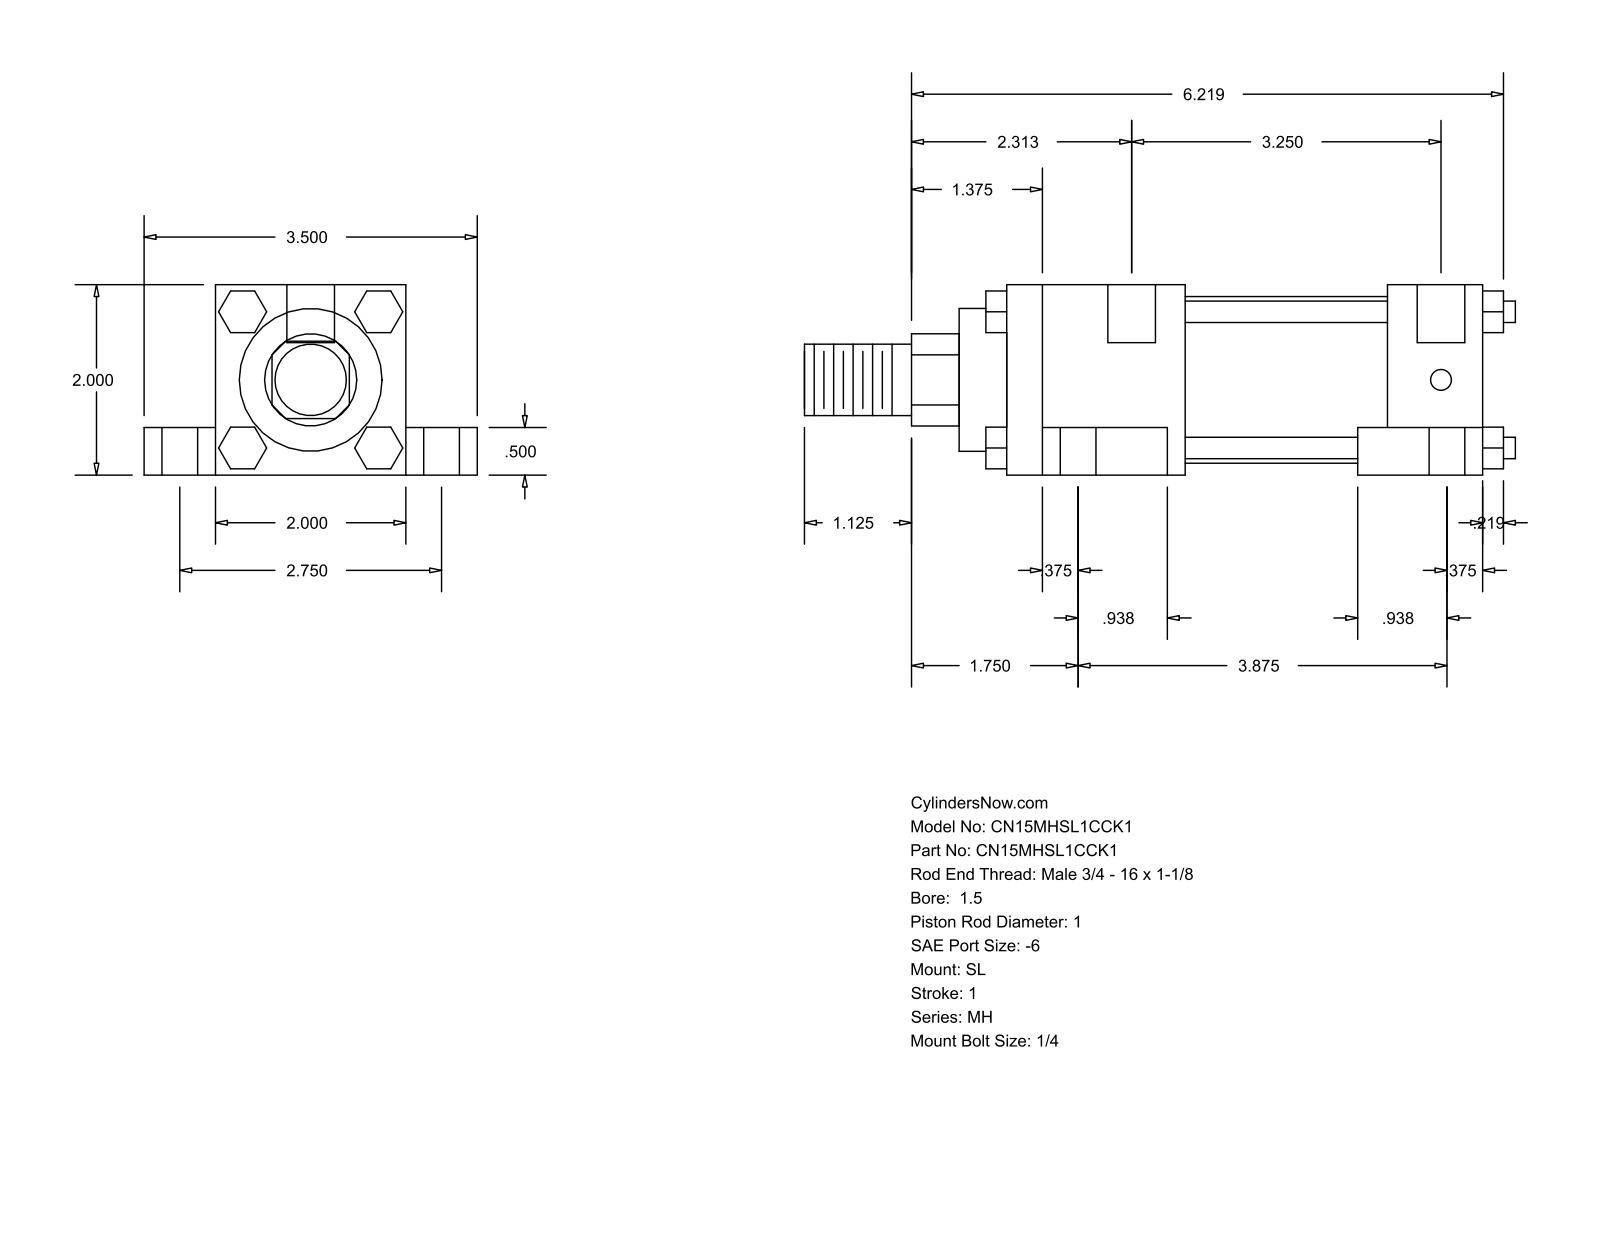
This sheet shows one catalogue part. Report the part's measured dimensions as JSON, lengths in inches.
{"part_name": "MH_SL__0150_1", "step_written_by": "GSSL Pune (CONFIG_CONTROL_DESIGN)", "units": "inches", "bodies": {"solids": 0, "faces": 148, "planar": 112, "cylindrical": 36, "other": 0}, "overall_size": [7.469, 3.5, 2], "round_holes": [[0.219, 4], [0.375, 4], [0.625, 4], [0.5, 2]], "round_bosses_or_shafts": [[0.225, 4], [1.75, 1], [1.5, 1], [1, 1], [0.75, 1]], "partial_cylinders_radius": [[0.484, 1]], "face_to_face_distances": [2, 0.5, 1.5, 0.75, 2.75, 4, 2.125, 5, 1, 0.375], "hole_center_spacings": [1.376, 1.443, 1.485, 2.75, 3.375, 3.587, 3.702, 3.875]}
